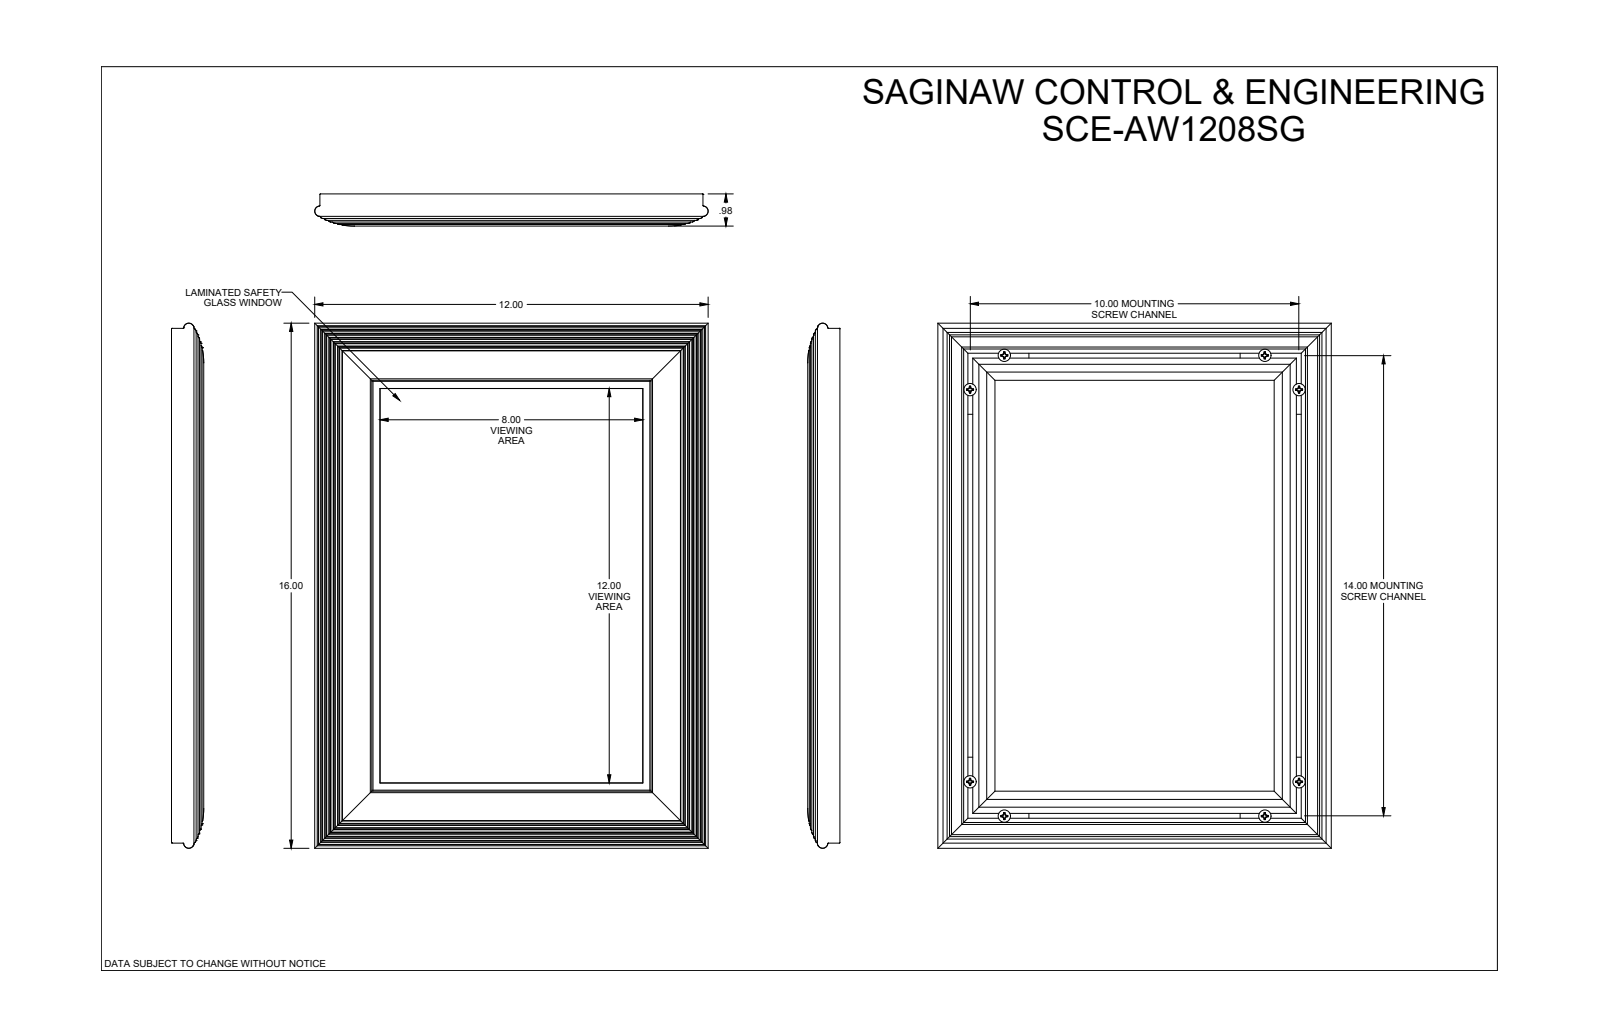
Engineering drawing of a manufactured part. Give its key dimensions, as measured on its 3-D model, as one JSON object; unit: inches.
{"part_name": "SCE-AW1208SG", "step_written_by": "SolidWorks 2019 (CONFIG_CONTROL_DESIGN)", "units": "inches", "bodies": {"solids": 25, "faces": 1202, "planar": 454, "cylindrical": 308, "other": 440}, "overall_size": [15.976, 11.976, 0.98], "volume_in3": 55.23, "surface_area_in2": 951.8, "round_holes": [[0.148, 8], [0.165, 4]], "round_bosses_or_shafts": [[0.19, 8], [0.122, 8]], "partial_cylinders_radius": [[0.02, 156], [0.059, 24], [0.01, 16], [0.03, 12], [0.016, 4], [0.02, 4], [0.06, 4], [0.157, 4]], "face_to_face_distances": [0.236, 0.06, 0.065, 0.075, 0.125, 0.216, 0.02, 1.52, 0.563, 0.141], "hole_center_spacings": [1.474, 9.033, 13.015, 15.774, 7.931, 10.016, 11.931, 14.016]}
